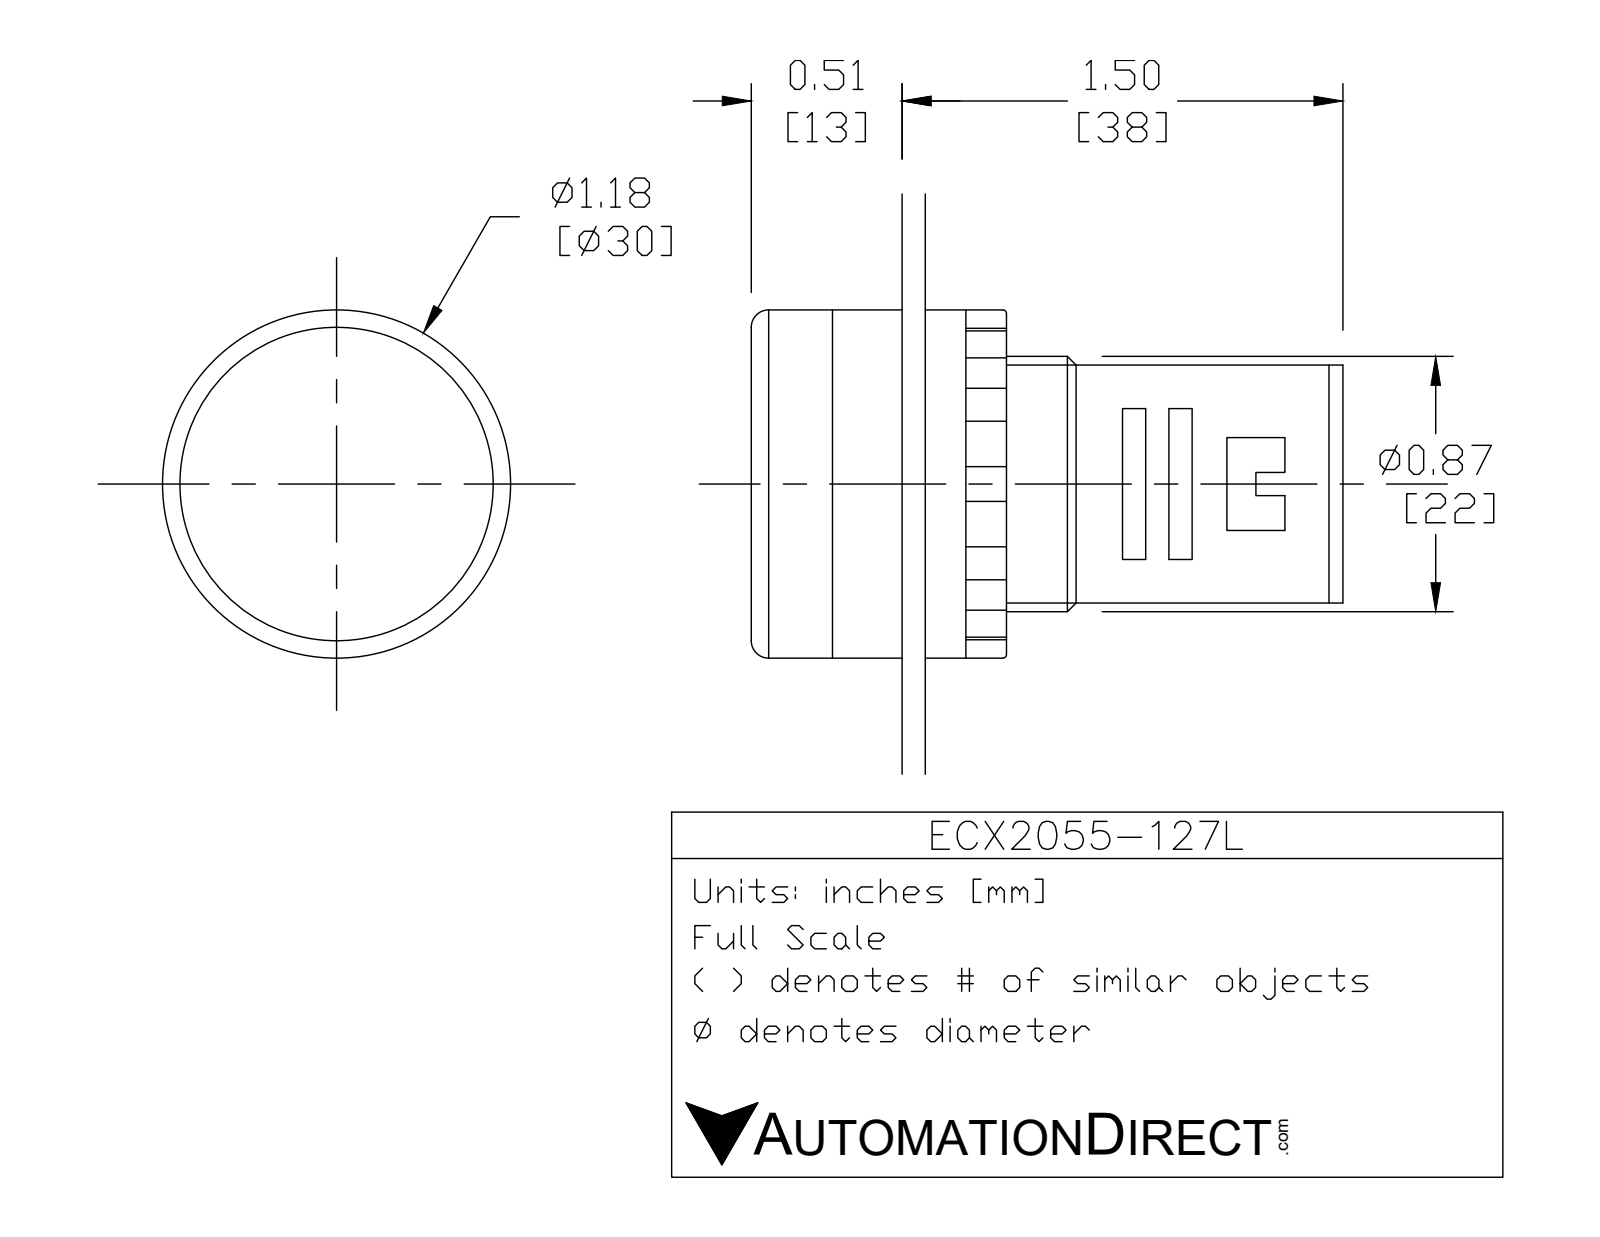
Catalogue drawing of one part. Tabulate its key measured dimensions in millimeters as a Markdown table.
| quantity | value |
| --- | --- |
| part name | ECX2055-127L |
| STEP written by | SolidWorks 2017 (AUTOMOTIVE_DESIGN) |
| units | millimeters |
| bodies | 6 solids, 123 faces (63 planar, 39 cylindrical, 21 other) |
| overall size | 51 × 30 × 30 |
| volume | 22 483 mm³ |
| surface area | 9 831 mm² |
| round holes (diameter × count) | 5.5 × 2, 22.5 × 1 |
| round bosses / shafts (diameter × count) | 4 × 2, 30 × 1, 29 × 1, 26.5 × 1, 22 × 1, 20 × 1 |
| partial cylindrical surfaces (radius × count) | 1 × 12 |
| main face-to-face distances | 6, 19, 13, 7, 2, 25, 4, 12, 17, 15 |
| hole center spacings | 4.62, 9.24 |
